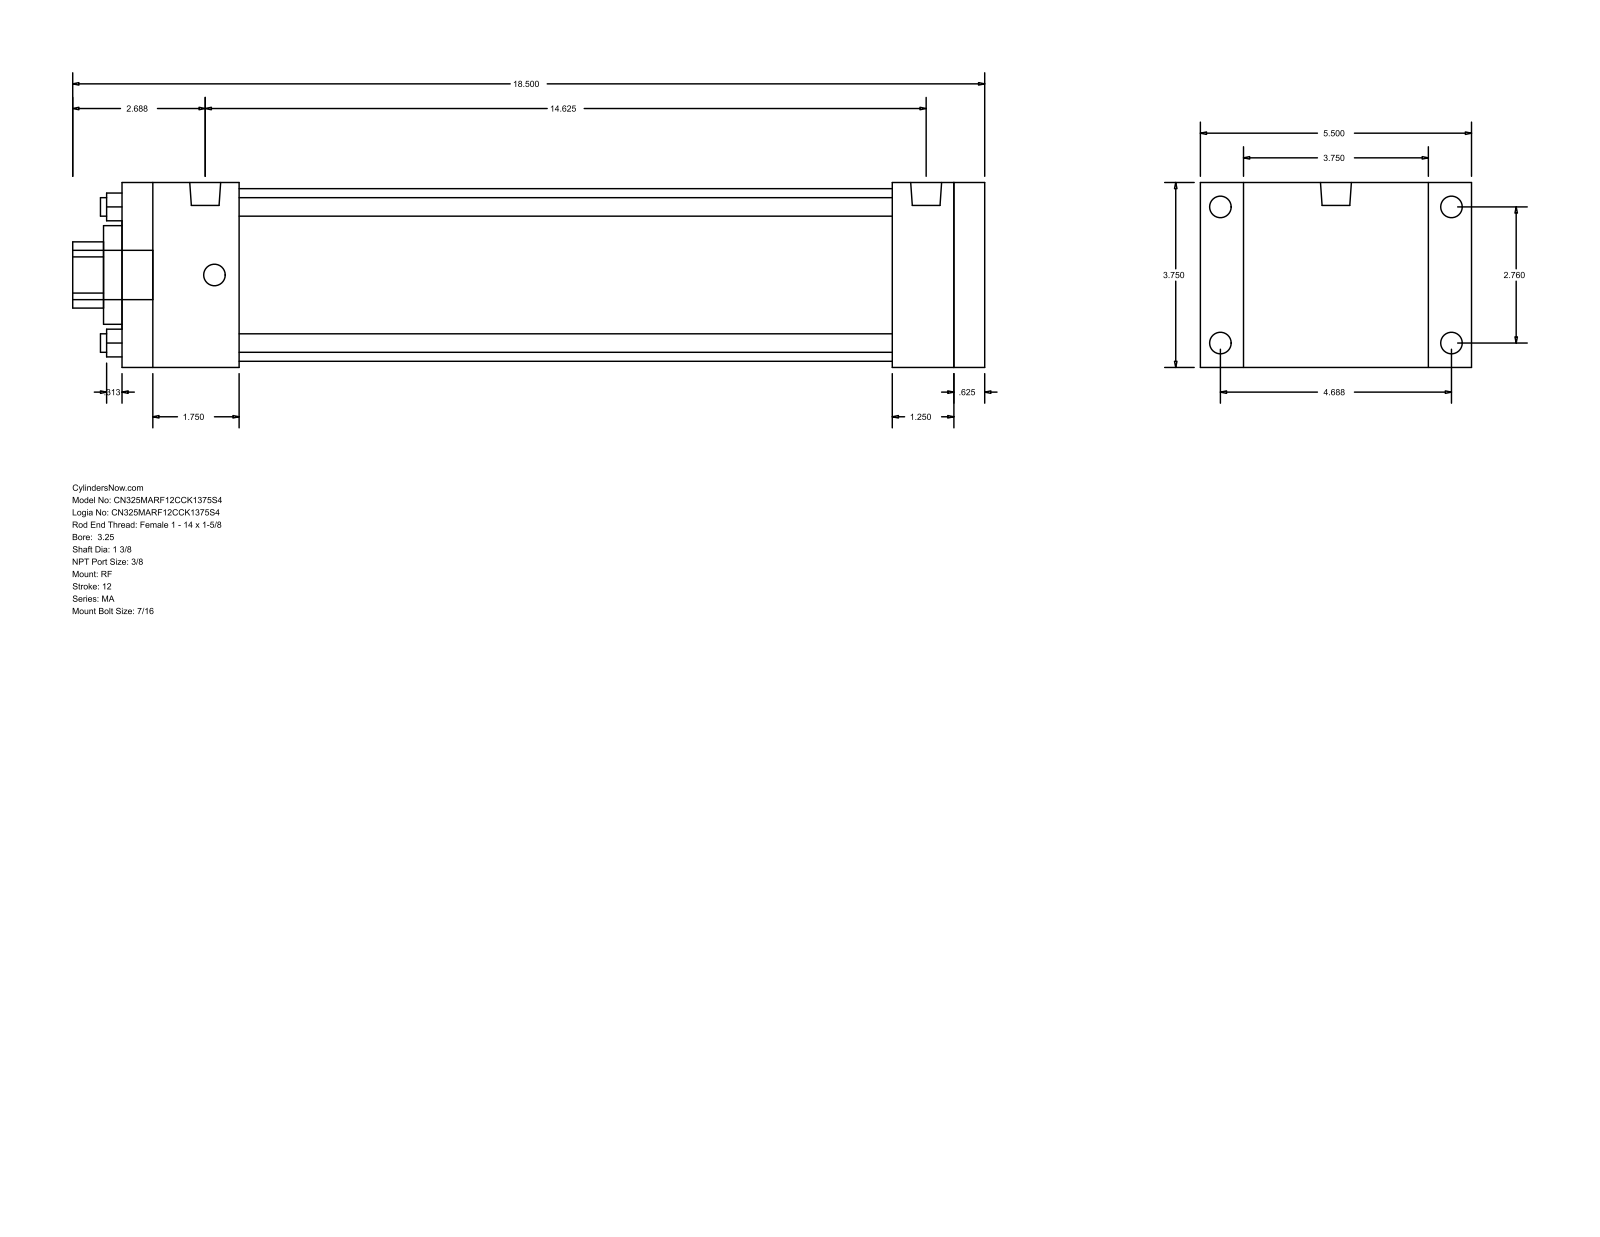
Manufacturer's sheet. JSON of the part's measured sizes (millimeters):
{"part_name": "MA_RF__0325_1.375", "step_written_by": "GSSL Pune (CONFIG_CONTROL_DESIGN)", "units": "millimeters", "bodies": {"solids": 0, "faces": 92, "planar": 64, "cylindrical": 28, "other": 0}, "overall_size": [469.9, 139.7, 95.25], "round_holes": [[9.53, 4], [34.92, 1], [50.8, 1], [88.9, 1]], "round_bosses_or_shafts": [[11.11, 8], [15.93, 2], [25.4, 1]], "partial_cylinders_radius": [[17.06, 1]], "face_to_face_distances": [95.24, 444.5, 15.88, 428.62, 22.23, 117.47, 396.87, 31.75, 47.63, 60.32], "hole_center_spacings": [49.57, 70.1, 99.14]}
